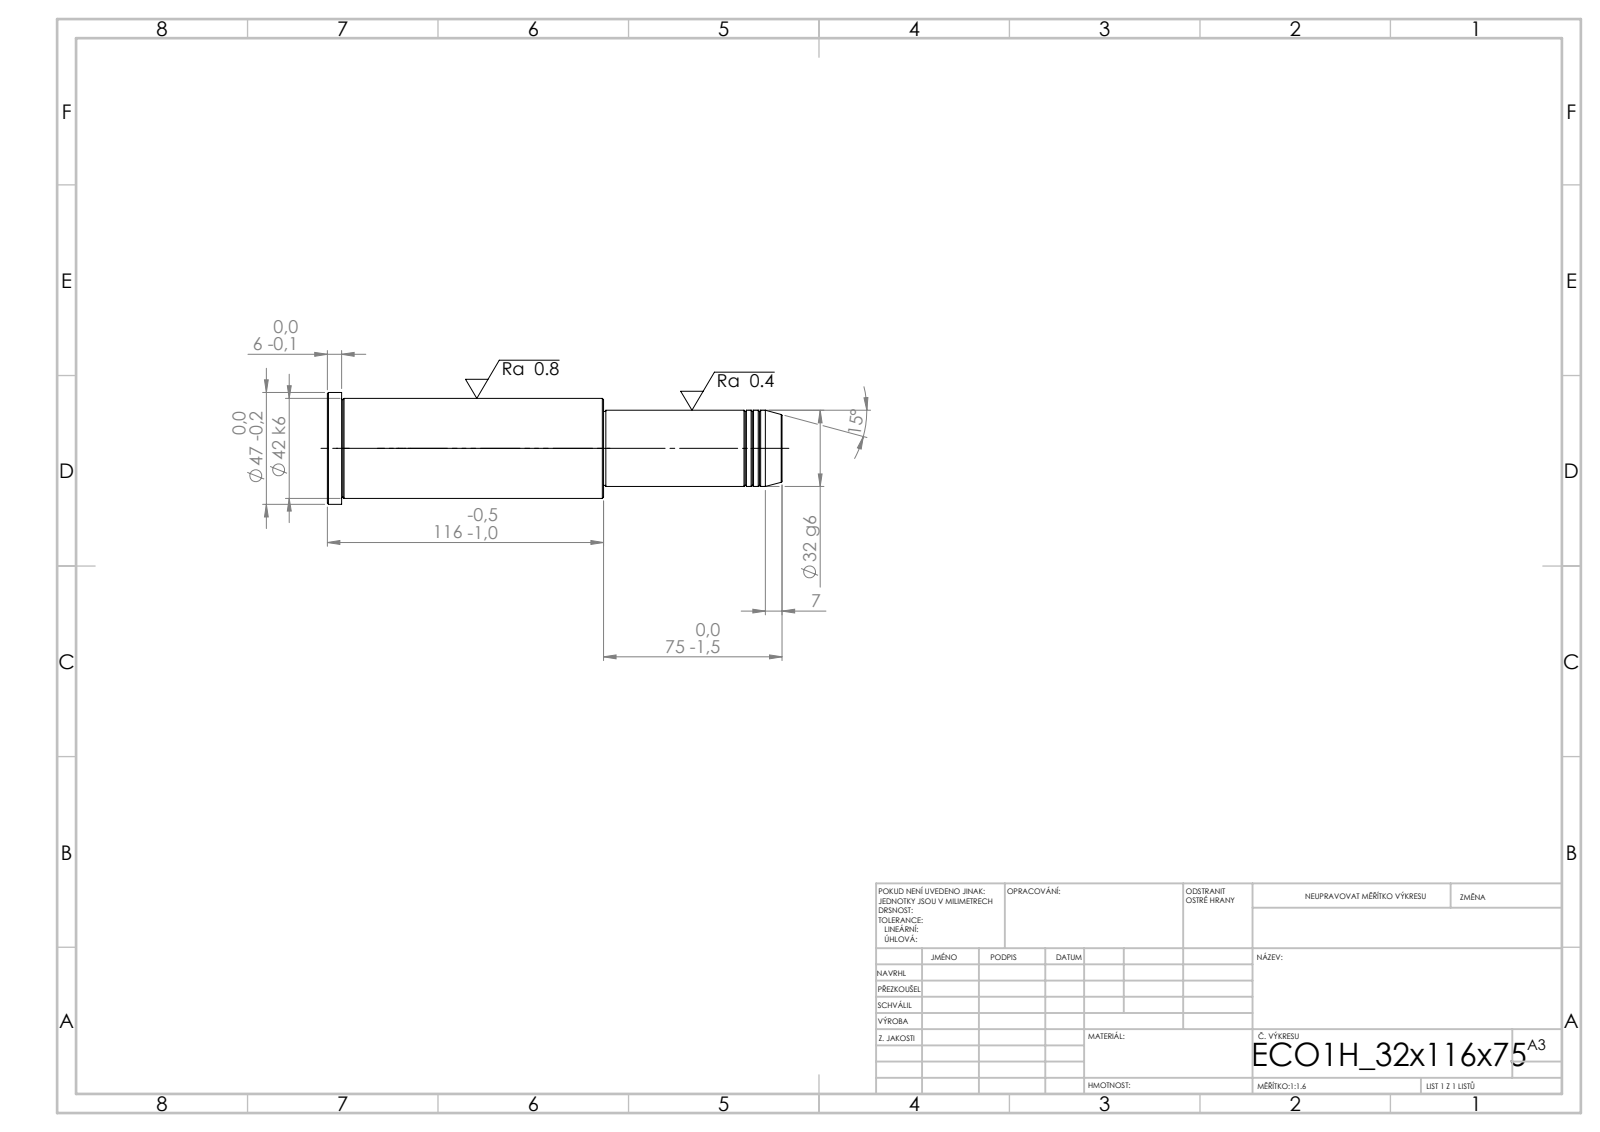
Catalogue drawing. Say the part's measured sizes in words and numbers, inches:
Its 3-D file was written by "SolidWorks 2019 (CONFIG_CONTROL_DESIGN)". It is 1 solid with 43 faces: 5 planar, 14 cylindrical and 24 other. Overall it measures 7.52 by 1.85 by 1.85 inches. Its volume is 13.56 cubic inches and its surface area 41 square inches. Round bosses or shafts: 1 of diameter 1.85, 1 of diameter 1.654, 1 of diameter 1.26, 1 of diameter 1.22. The main face-to-face distances are 7.52, 2.953, 4.567, 7.283, 4.331, 0.236, 2.913, 0.039, 4.37, 4.606.
